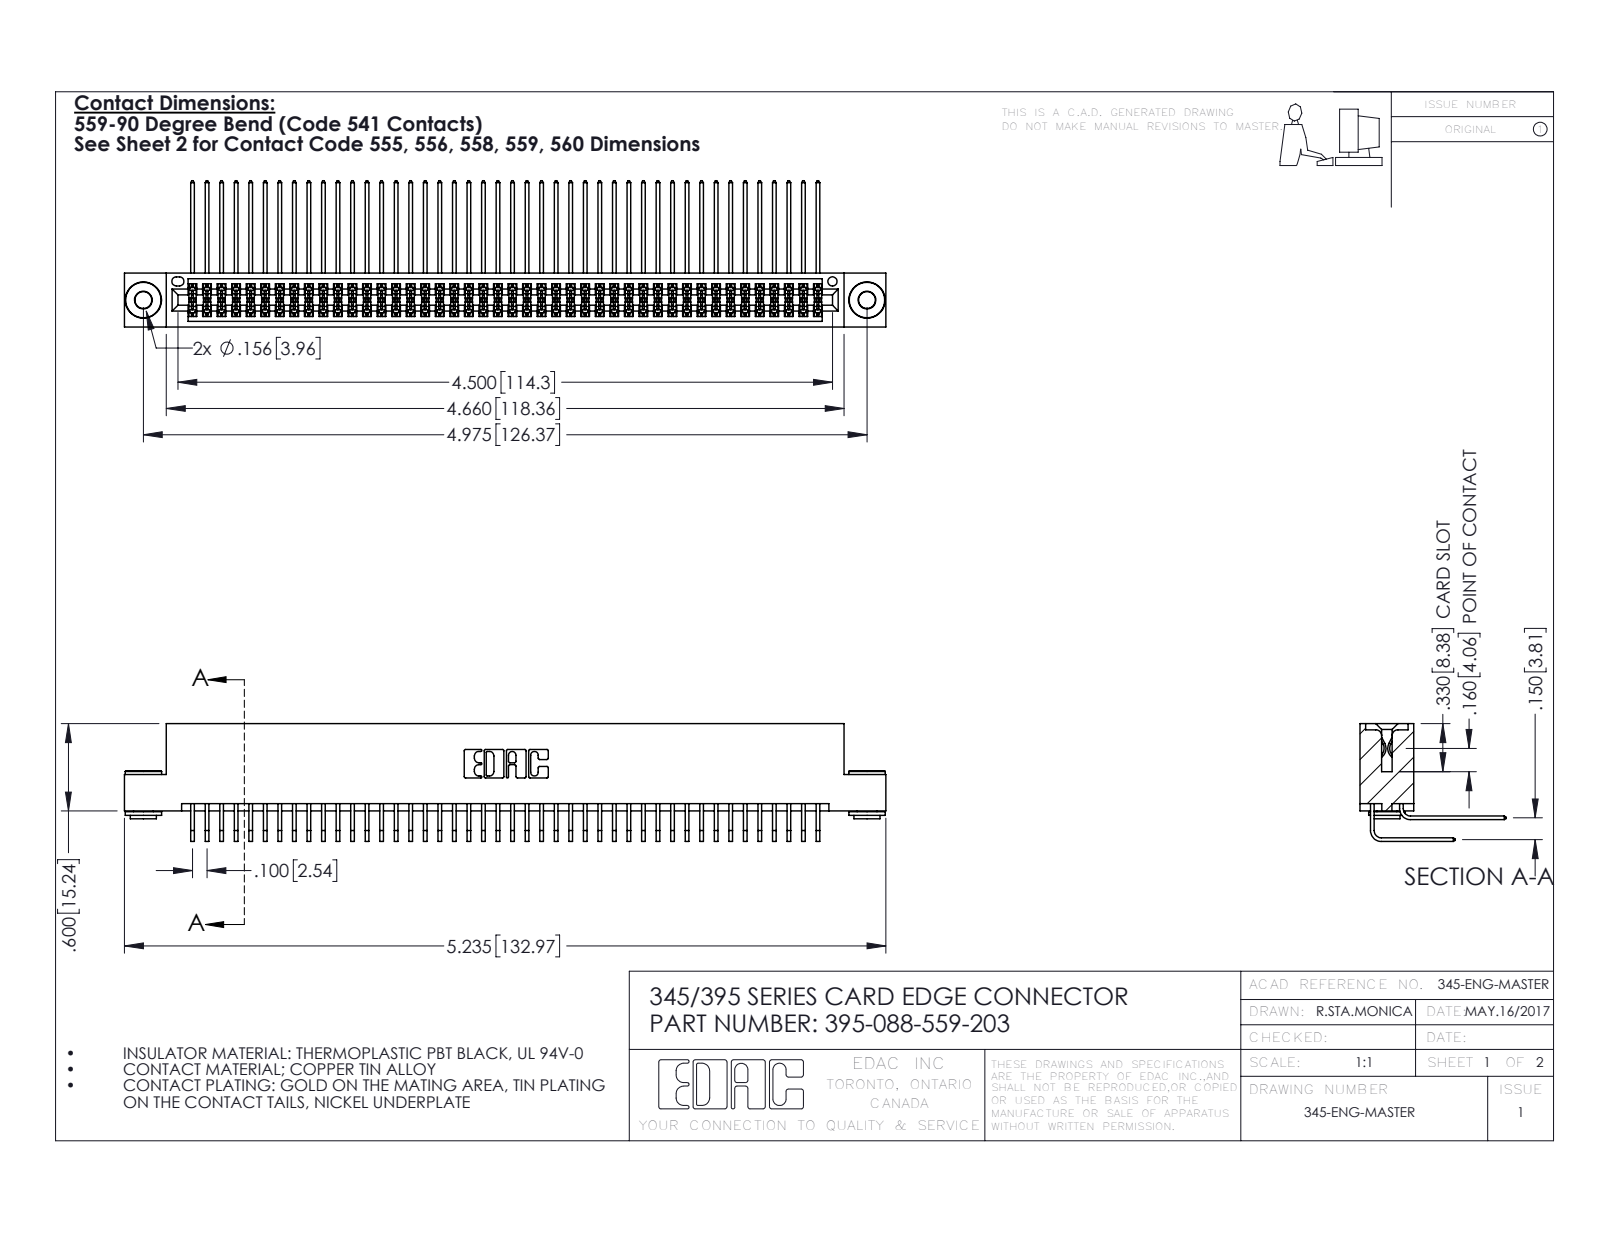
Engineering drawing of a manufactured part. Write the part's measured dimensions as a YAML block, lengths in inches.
part_name: "345-292-001_558 559 Tail - 1; 345-250-002_345-250-002-102; 395-088-559-203; 345 Part_Flush Mounting Lugs - 0.156 Dia-TH (+1 more)"
step_written_by: "SolidWorks 2016 (CONFIG_CONTROL_DESIGN)"
units: inches
bodies: {solids: 91, faces: 4740, planar: 3170, cylindrical: 1562, other: 8}
overall_size: [5.235, 1.005, 0.809]
volume: 0.822
surface_area: 34.92
round_holes:
  - {diameter: 0.116, count: 2}
  - {diameter: 0.156, count: 2}
  - {diameter: 0.064, count: 1}
round_bosses_or_shafts:
  - {diameter: 0.25, count: 2}
  - {diameter: 0.18, count: 2}
  - {diameter: 0.136, count: 2}
partial_cylinders:
  - {radius: 0.006, count: 133}
  - {radius: 0.01, count: 22}
  - {radius: 0.007, count: 6}
  - {radius: 0.031, count: 6}
  - {radius: 0.026, count: 3}
  - {radius: 0.014, count: 2}
  - {radius: 0.019, count: 2}
  - {radius: 0.022, count: 2}
face_to_face_distances: [0.072, 0.298, 0.2, 0.37, 0.025, 0.098, 0.272, 0.225, 0.175, 0.15]
hole_center_spacings: [0.27, 4.739, 4.975]
